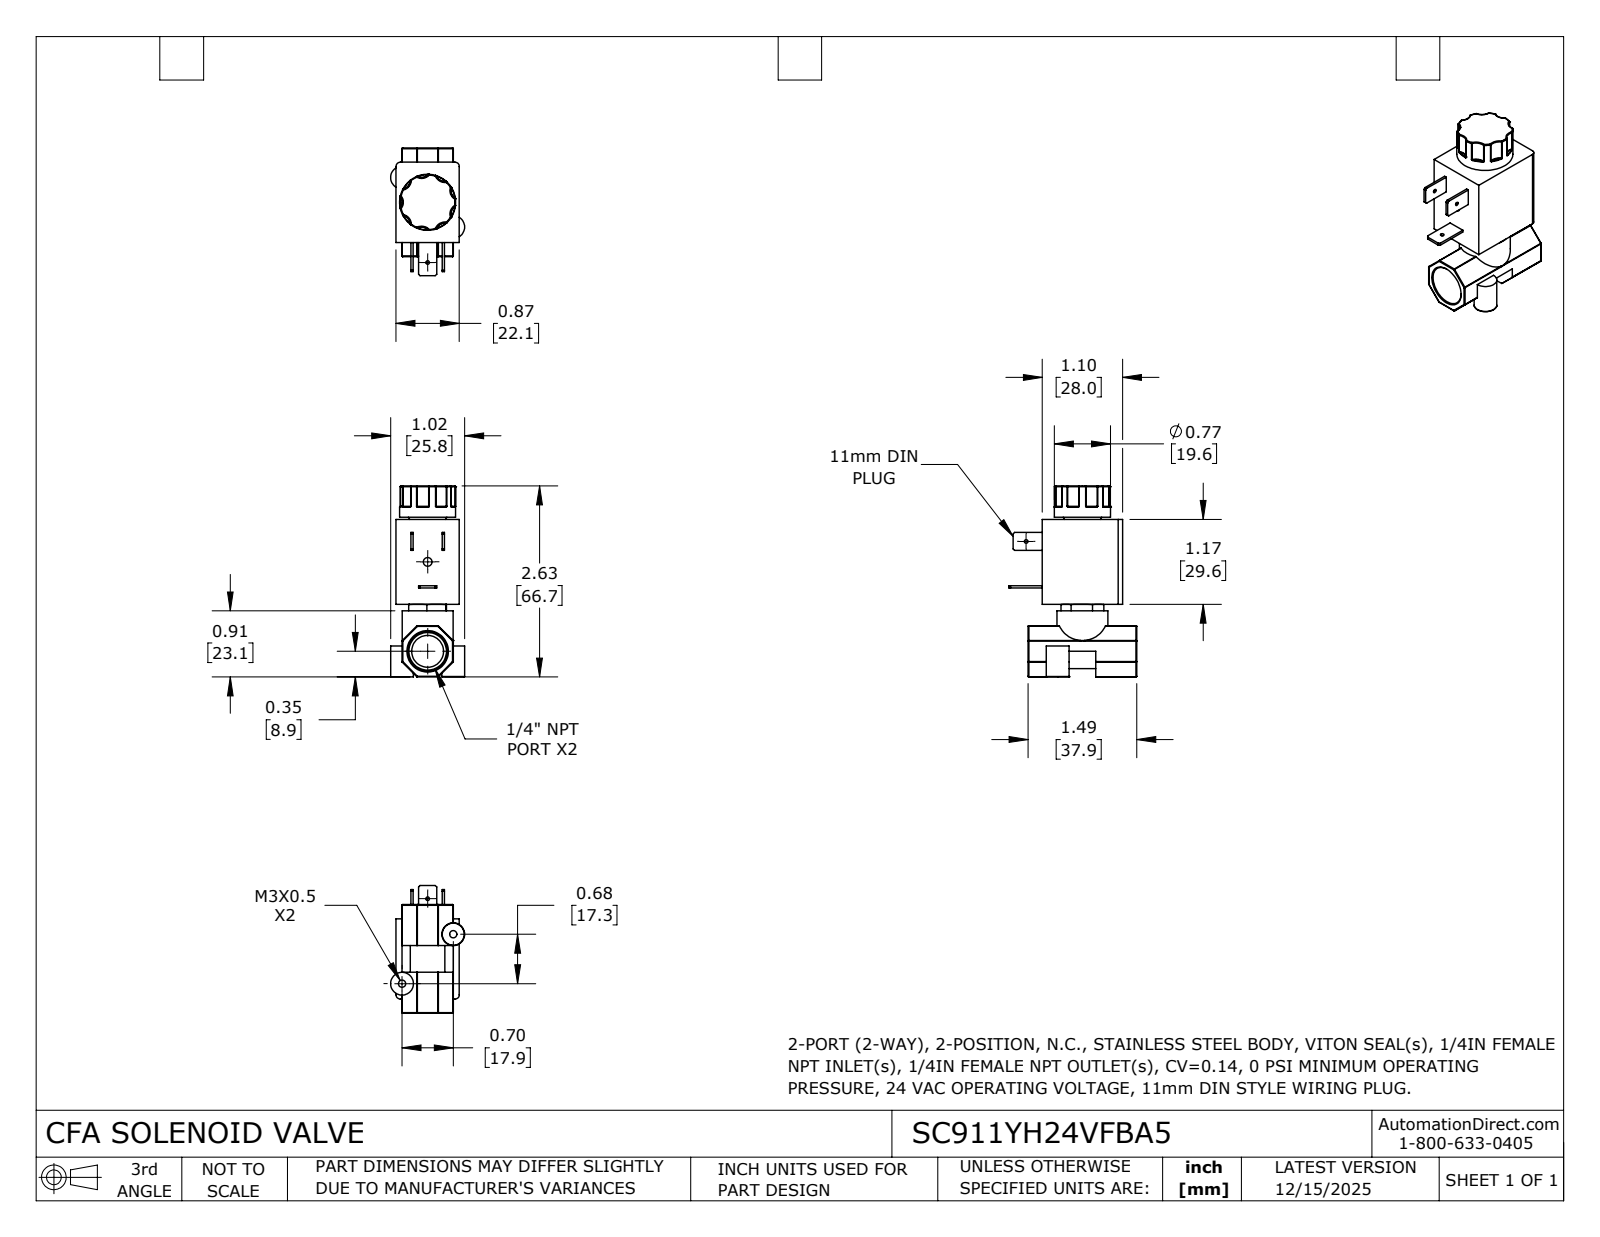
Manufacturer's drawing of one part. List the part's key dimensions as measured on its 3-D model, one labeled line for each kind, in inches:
Part name (STEP PRODUCT): SC911YH24VFBA5
STEP written by: SolidWorks 2024 (CONFIG_CONTROL_DESIGN)
Units: inches
Bodies: 1 solid, 312 faces (74 planar, 89 cylindrical, 149 other)
Overall size (bounding box): 2.625 × 1.757 × 1.017
Volume: 1.799 in³ · Surface area: 16.13 in²
Round holes (diameter × count): ⌀0.05 ×2, ⌀0.1 ×2, ⌀0.12 ×1, ⌀0.438 ×1
Round bosses / shafts (diameter × count): ⌀0.313 ×2, ⌀0.77 ×1, ⌀0.7 ×1
Partial cylindrical surfaces — rounded edges, fillets, slot ends (radius × count): R0.01 ×42, R0.133 ×7, R0.06 ×2, R0.132 ×2, R0.237 ×1
Main face-to-face distances: 0.87, 0.704, 1.104, 1.167, 0.083, 0.787, 0.46, 0.998, 2.165, 2.625
Hole centre spacings: 0.602, 0.979, 1.22, 1.23
